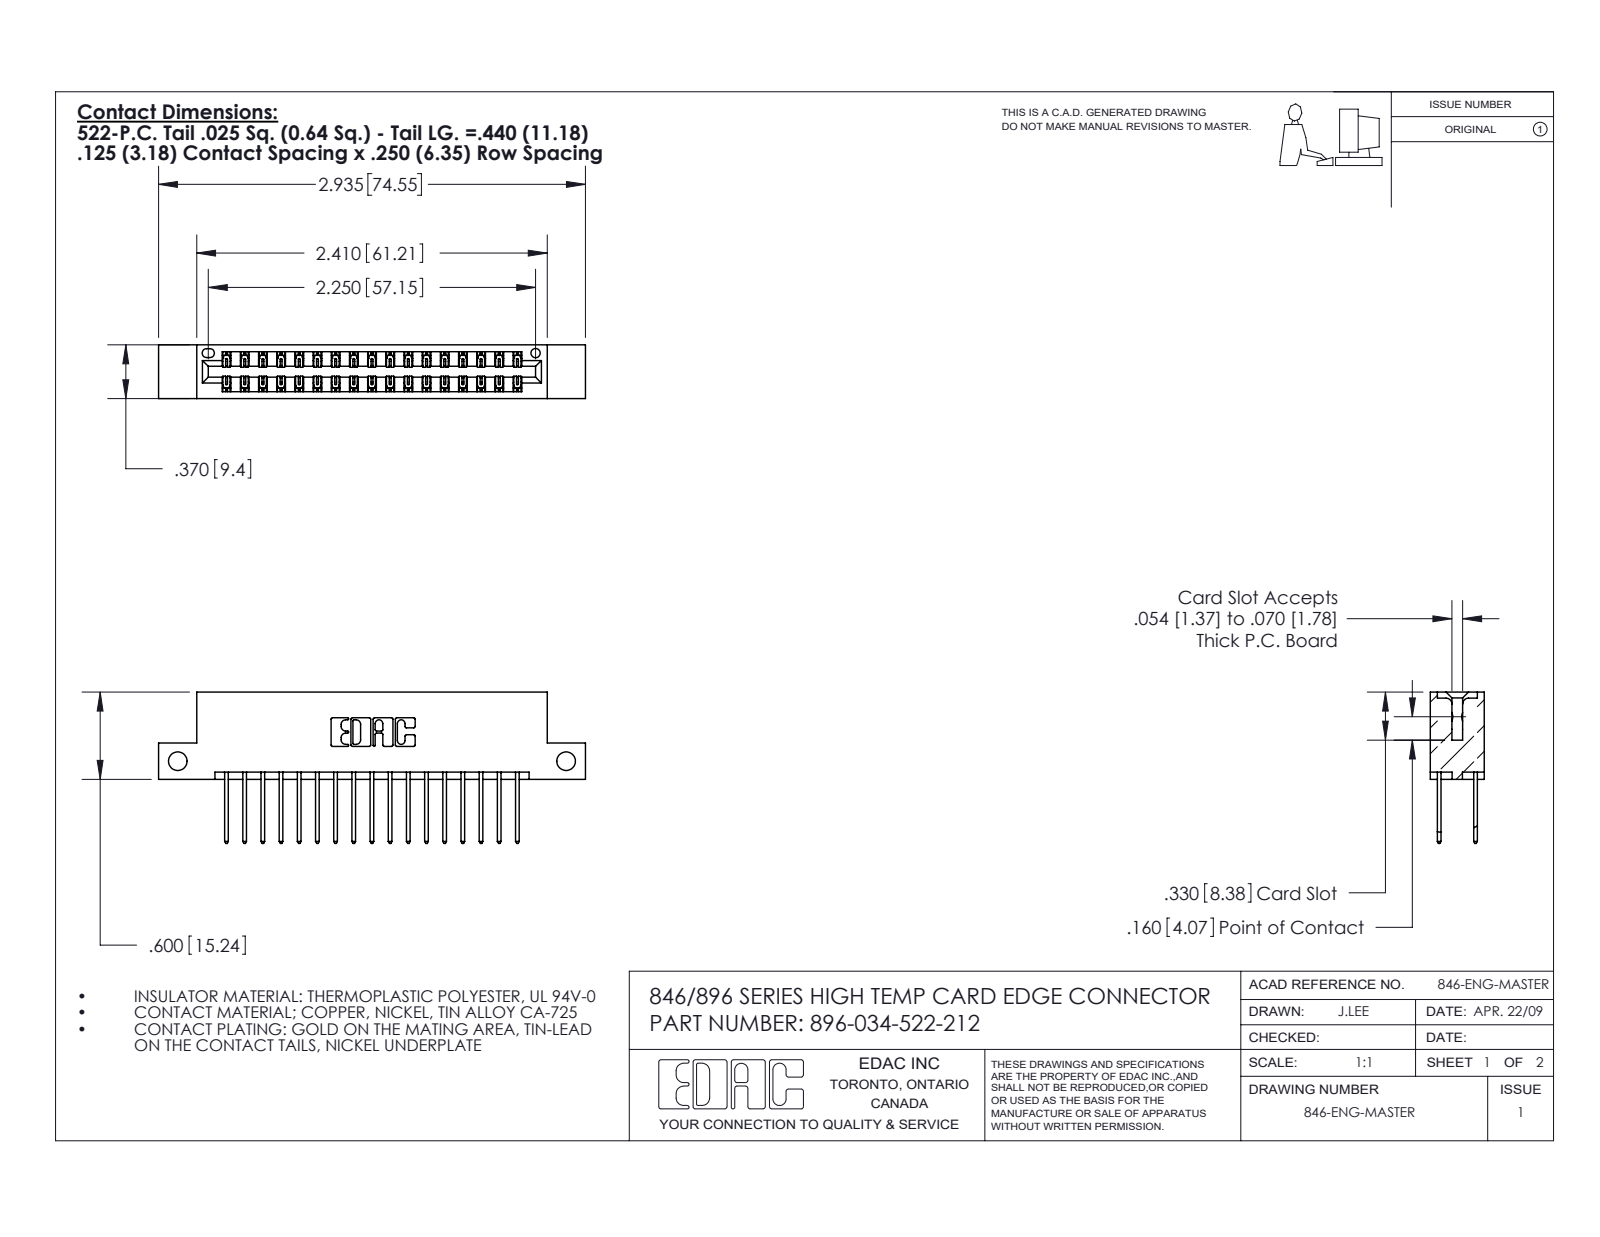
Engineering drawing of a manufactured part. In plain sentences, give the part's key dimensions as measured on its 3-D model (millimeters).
The part is named "345-292-001_345-293-122; 396-034-522-212; 346 Part_Flush Mounting Lugs - Side Mount". Its 3-D file was written by "SolidWorks 2016 (CONFIG_CONTROL_DESIGN)". It is 35 solids with 1890 faces: 1266 planar, 624 cylindrical and 0 other. Overall it measures 74.5 by 26.4 by 9.4 millimeters. Its volume is 7 080 cubic millimeters and its surface area 9 600 square millimeters. Round holes: 2 of diameter 3.3, 1 of diameter 1.6. Partial cylindrical surfaces (rounded edges, fillets, slot ends): 51 of radius 0.2, 34 of radius 0.3, 22 of radius 0.3, 6 of radius 0.2, 6 of radius 0.8, 3 of radius 0.7, 2 of radius 0.4, 2 of radius 0.6. The main face-to-face distances are 1.2, 8.2, 6.4, 9.4, 1.8, 7.6, 0.6, 7, 3.8, 5.6. The hole center spacings are 67.8.
